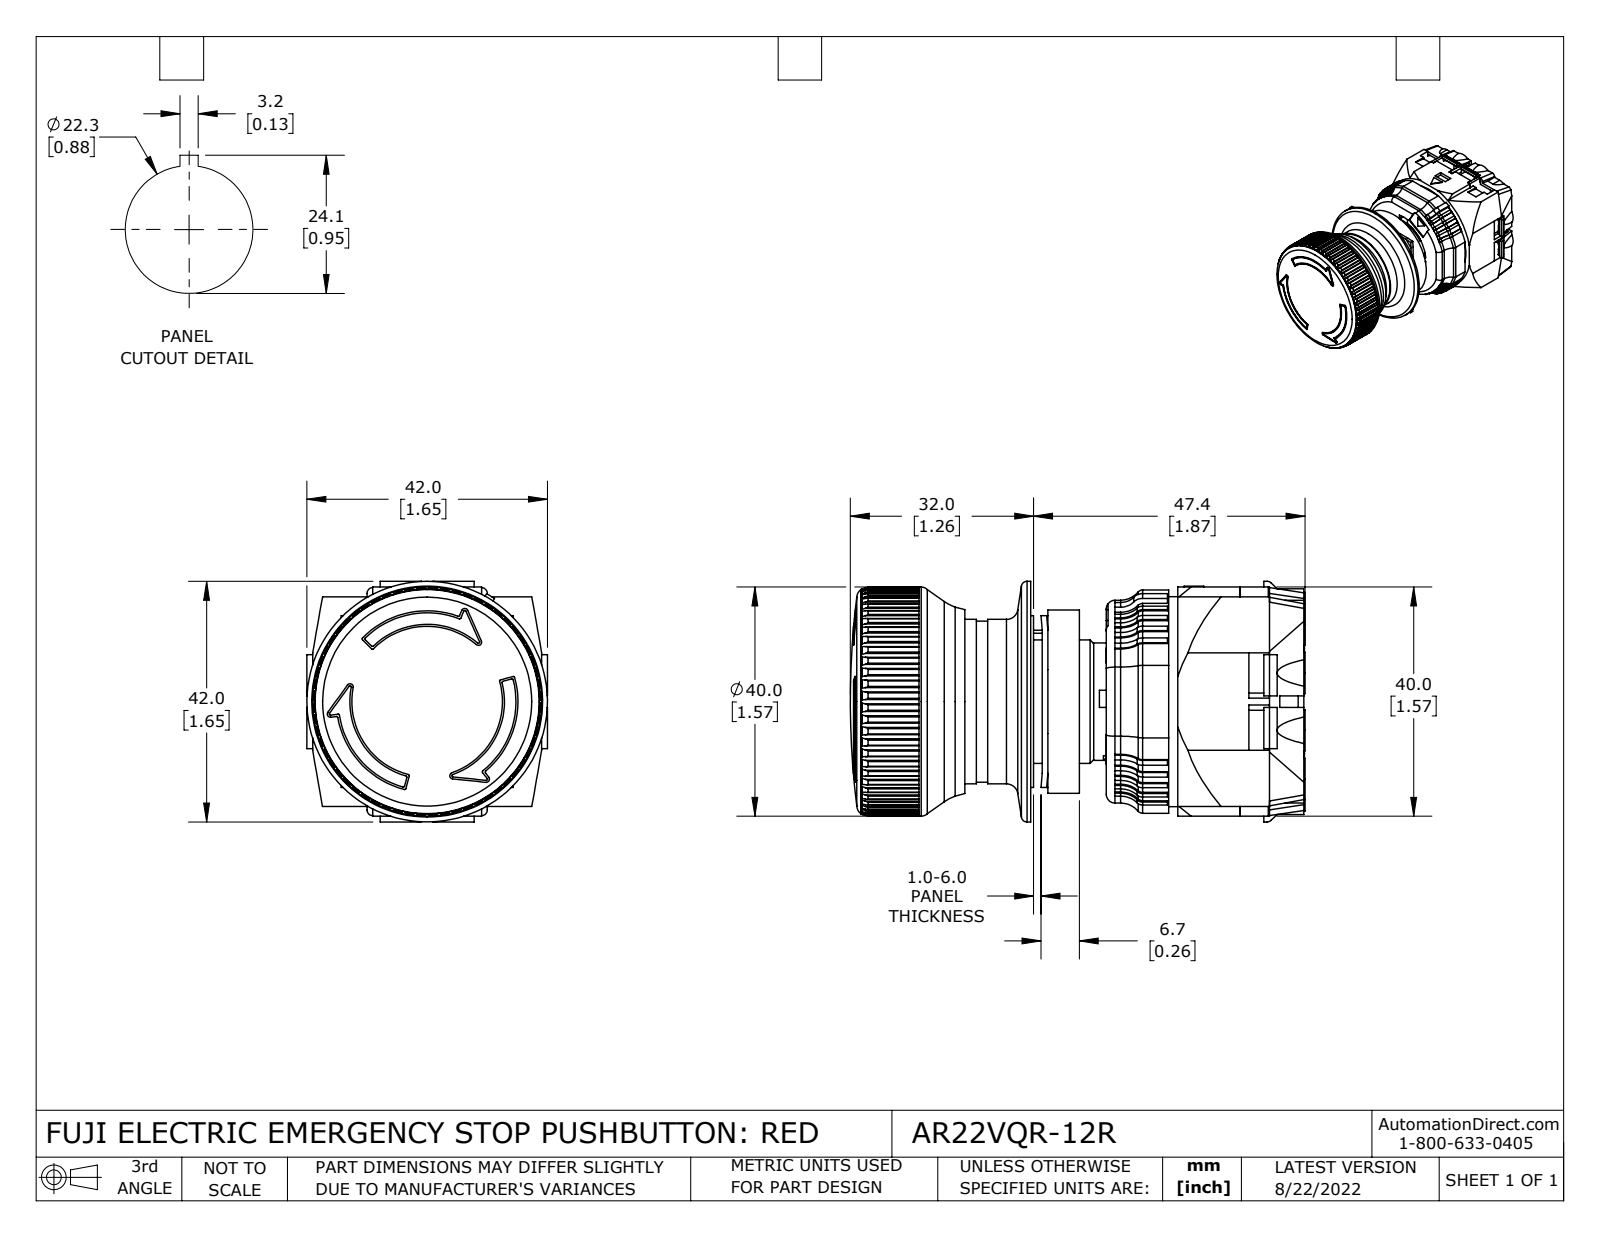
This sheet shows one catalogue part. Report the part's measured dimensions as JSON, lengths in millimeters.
{"part_name": "AR22VQR-12R", "step_written_by": "SolidWorks 2021 (CONFIG_CONTROL_DESIGN)", "units": "millimeters", "bodies": {"solids": 8, "faces": 2051, "planar": 1237, "cylindrical": 600, "other": 214}, "overall_size": [79.4, 42, 42], "volume_mm3": 62430, "surface_area_mm2": 34720, "round_holes": [[3.5, 12], [6.2, 12], [8, 1], [17.5, 1], [21, 1], [21.3, 1], [22, 1], [22.3, 1], [28, 1], [29.7, 1], [36.7, 1]], "round_bosses_or_shafts": [[7.2, 12], [42, 1], [40, 1], [32, 1], [30, 1], [28.7, 1], [28.1, 1], [22.4, 1]], "partial_cylinders_radius": [[0.2, 146], [0.4, 64], [1.2, 19], [3.8, 19], [4.2, 12], [1, 10], [0.6, 6], [1.5, 4]], "face_to_face_distances": [1, 18.5, 11.5, 10, 44.7, 18, 21, 3, 23.6, 4], "hole_center_spacings": [16.3, 23, 8.3, 8.9, 10, 14.9, 18.1, 18.7]}
